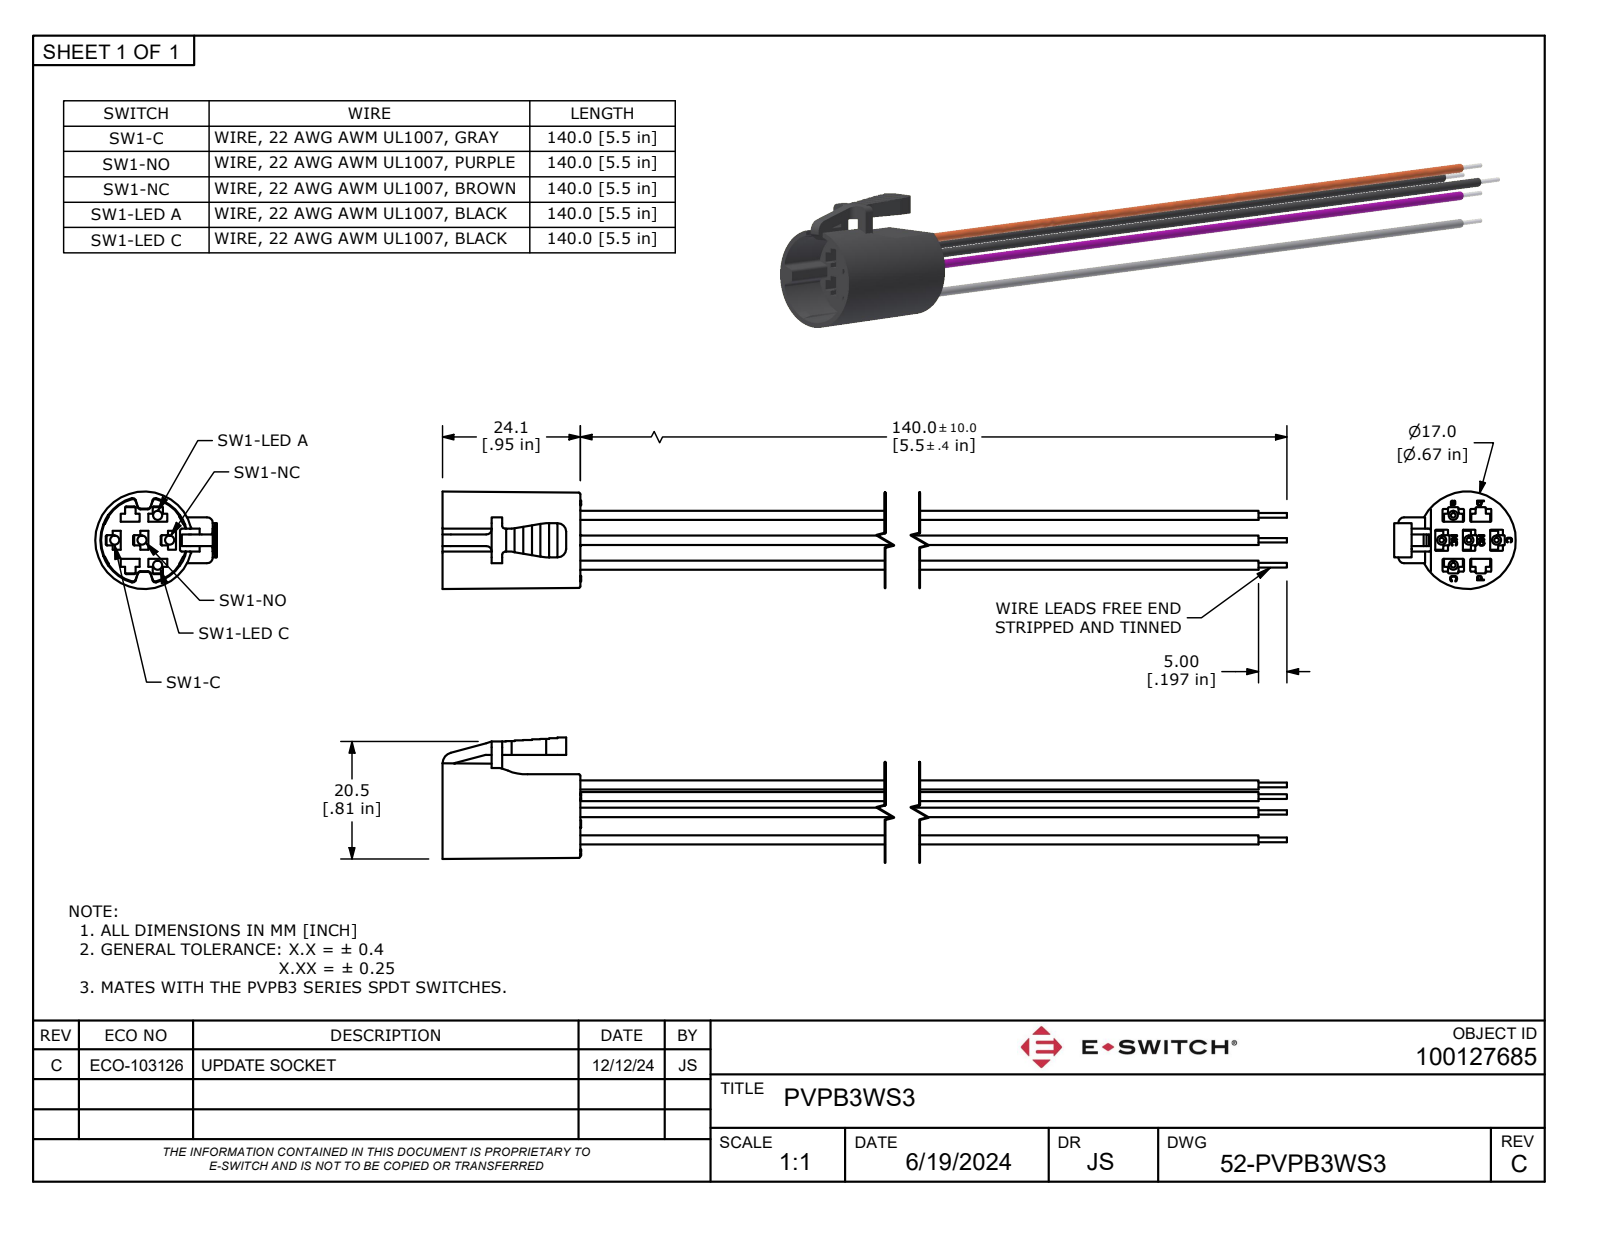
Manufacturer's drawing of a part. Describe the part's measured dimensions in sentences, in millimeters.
The part is named "PVPB3WS3". Its 3-D file was written by "Autodesk Inventor 2022 (AUTOMOTIVE_DESIGN)". It is 6 solids with 727 faces: 557 planar, 10 cylindrical and 160 other. Overall it measures 164.1 by 21.2 by 17 millimeters. Its volume is 3 650 cubic millimeters and its surface area 7 155 square millimeters. Round bosses or shafts: 5 of diameter 1.6, 5 of diameter 0.8. The main face-to-face distances are 4.8, 15.5, 5, 3.7, 0.8, 4.4, 5.1, 1.4, 4, 2.2.
